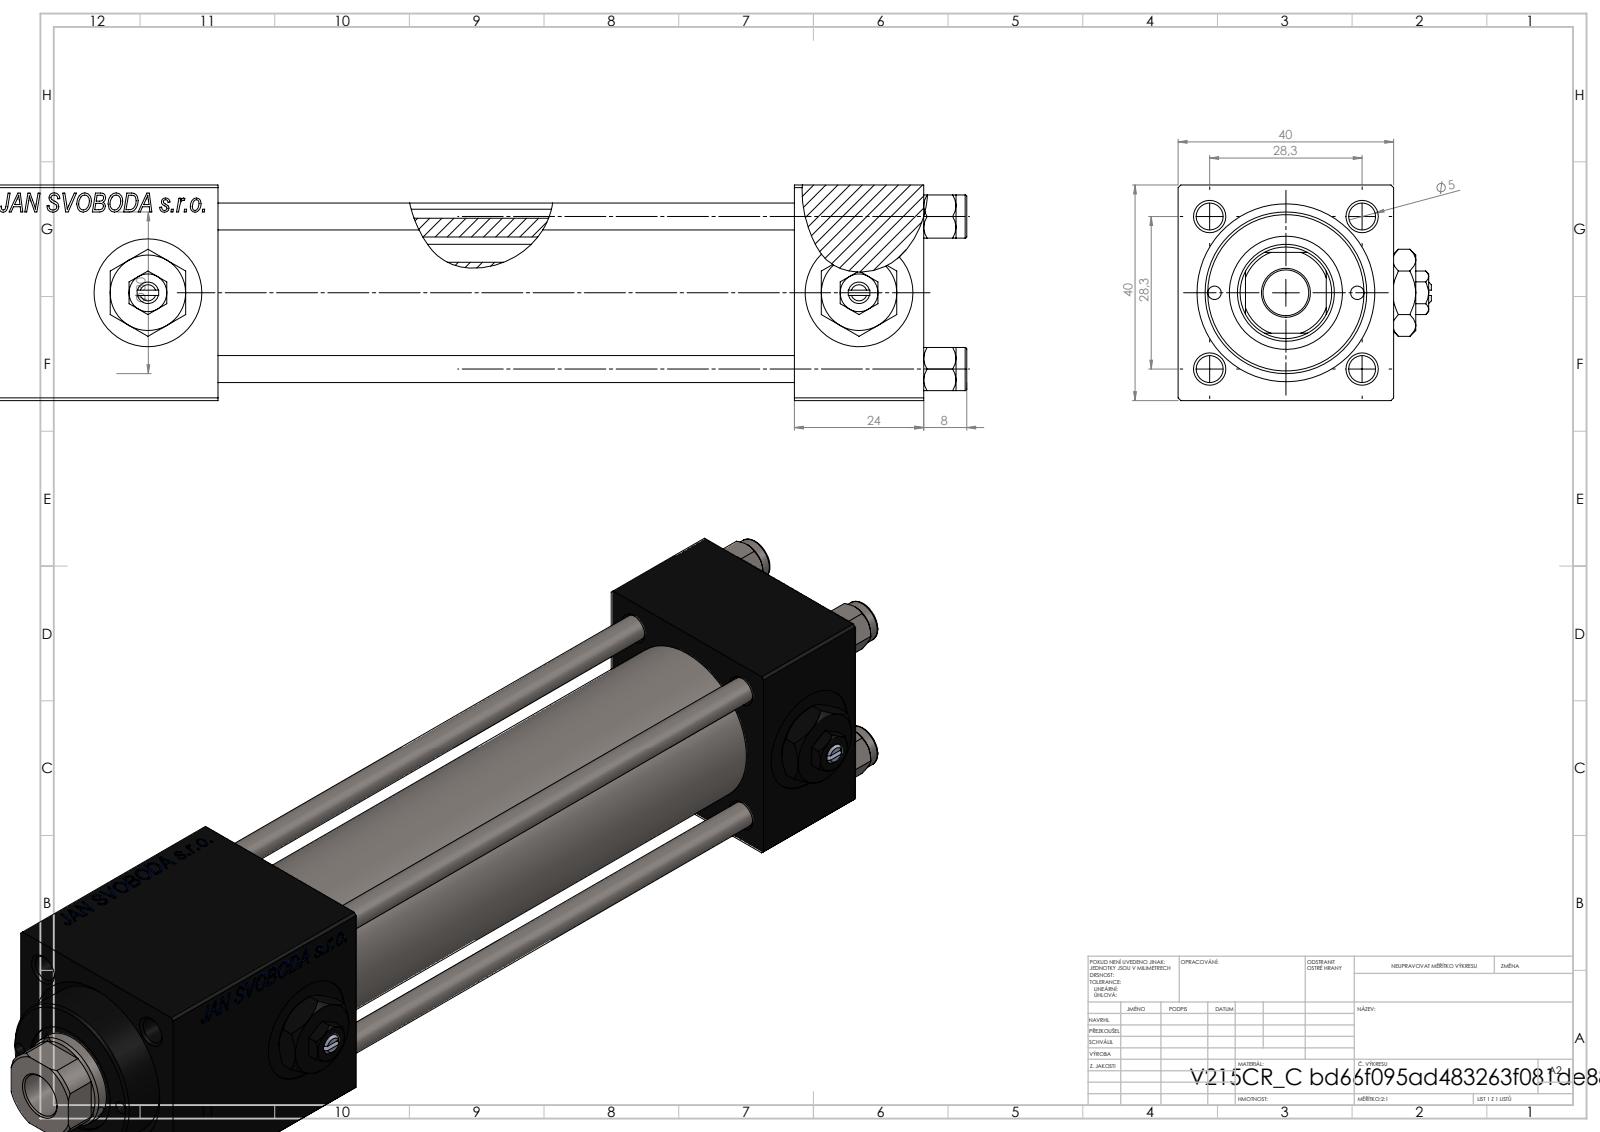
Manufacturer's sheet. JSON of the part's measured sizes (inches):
{"part_name": "V215CR_VCP_C; V215CR_C_Body; Zatka_pro_OIL_PORT; NUT_M5_C (+2 more)", "step_written_by": "SolidWorks 2019 (CONFIG_CONTROL_DESIGN)", "units": "inches", "bodies": {"solids": 8, "faces": 164, "planar": 44, "cylindrical": 24, "other": 96}, "overall_size": [6.063, 1.478, 1.429], "volume_in3": 0.803, "surface_area_in2": 17.63, "round_holes": [[0.197, 4]], "round_bosses_or_shafts": [[0.315, 4]], "face_to_face_distances": [0.315, 0.965, 0.557, 0.242, 0.872, 1.28, 1.522, 0.65, 0.408, 1.114], "hole_center_spacings": [1.114, 1.576]}
